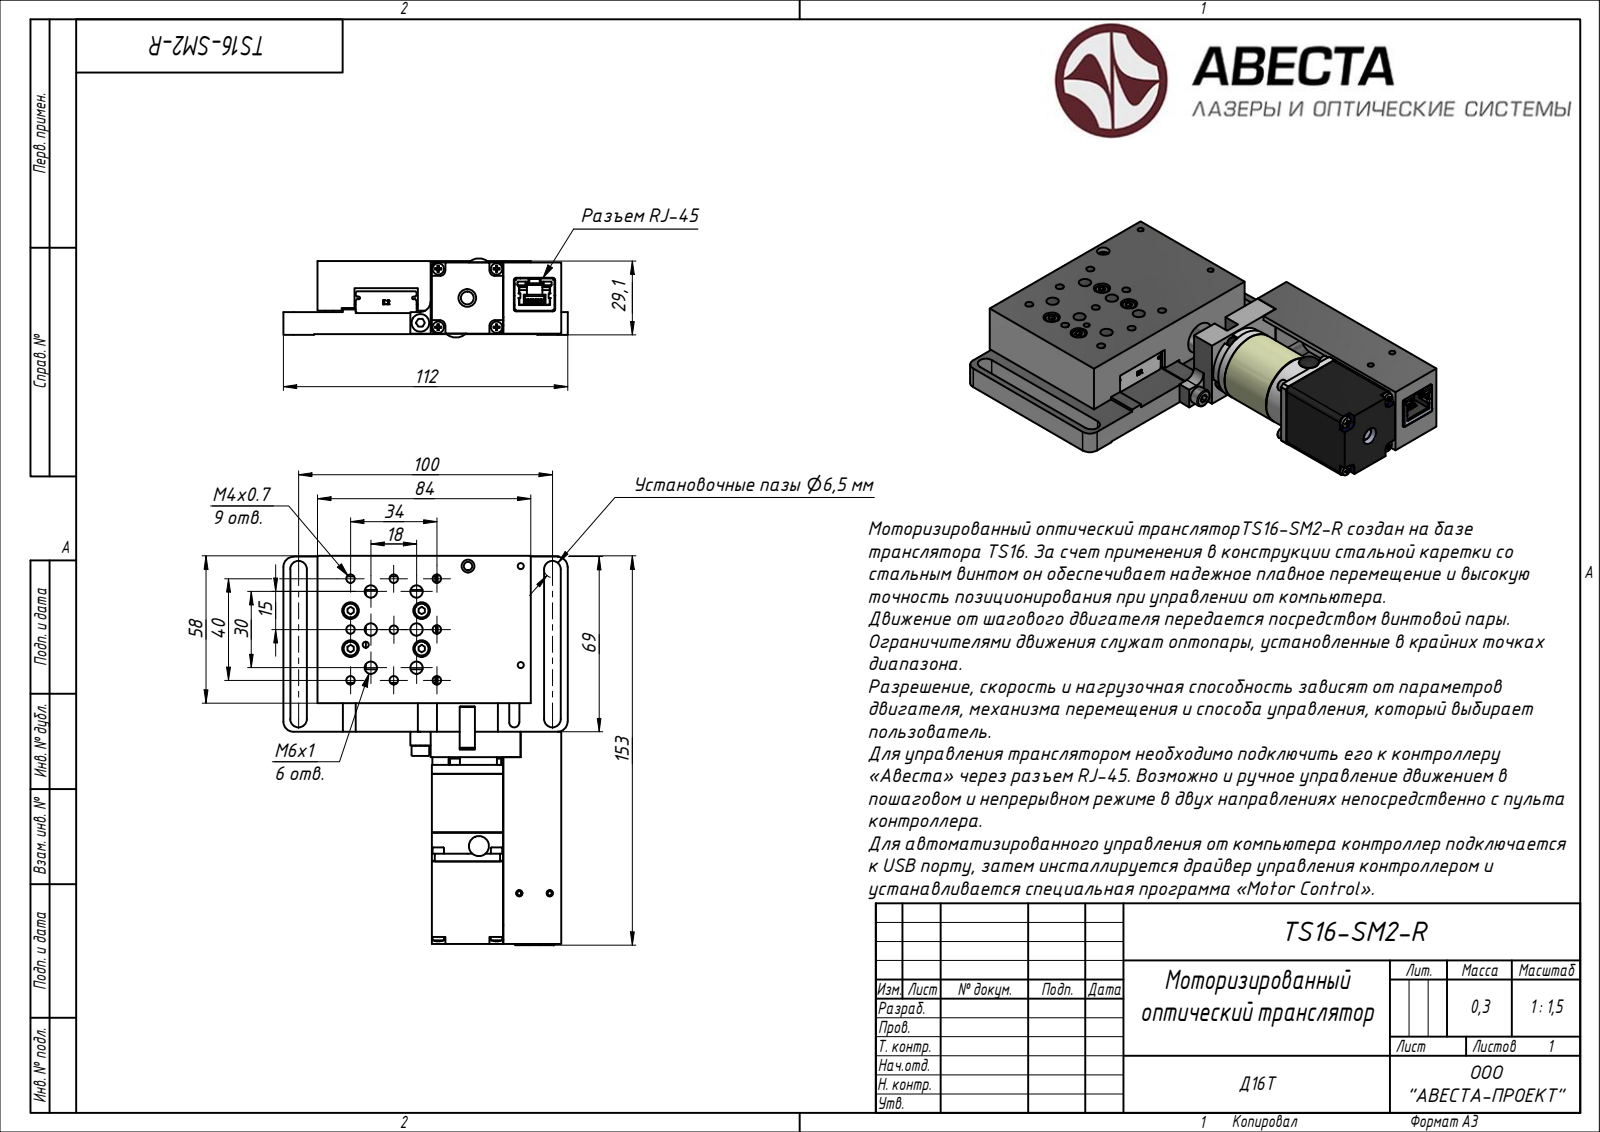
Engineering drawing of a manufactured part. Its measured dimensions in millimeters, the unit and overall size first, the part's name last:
Units: millimetres
Overall size (bounding box): 153.26 × 112 × 31.2
Bodies: 27 solids, 2882 faces (0 planar, 0 cylindrical, 2882 other)
Part name (STEP PRODUCT): Block 01; Block 02
STEP written by: ST-DEVELOPER v15 (AUTOMOTIVE_DESIGN)
